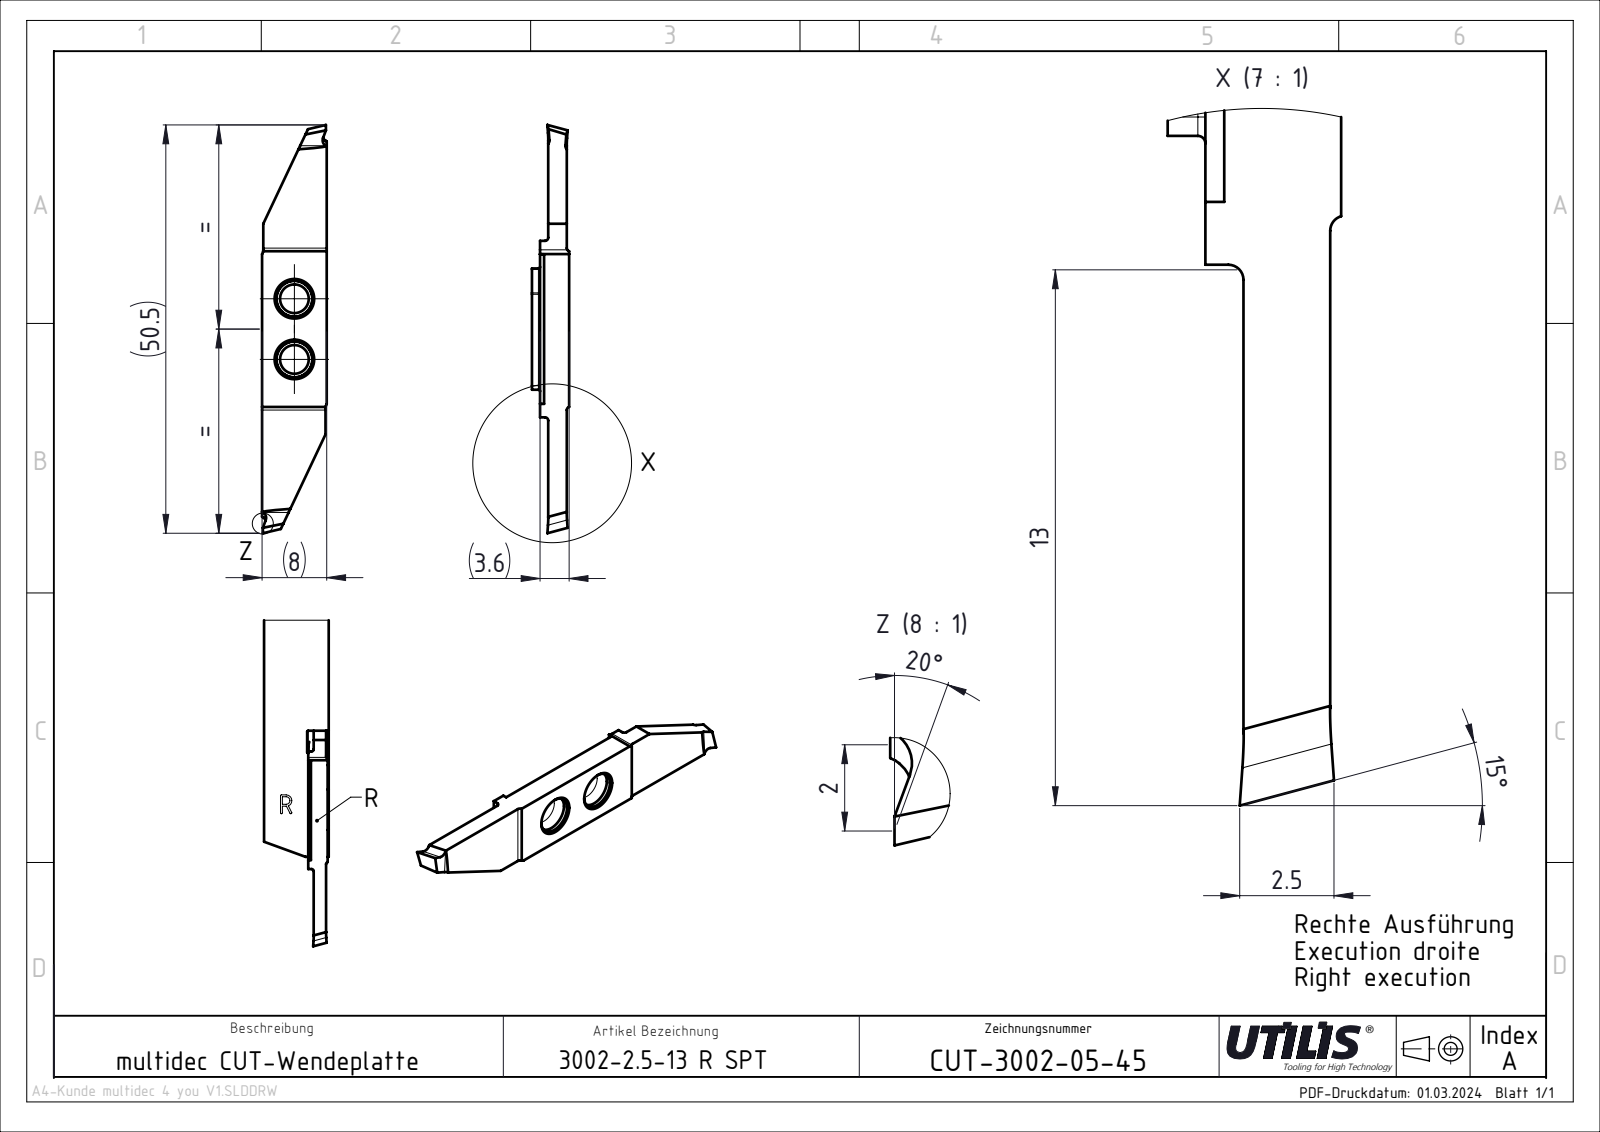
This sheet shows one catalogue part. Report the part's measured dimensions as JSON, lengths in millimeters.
{"part_name": "CUT-3002 SPT Slim_and_Deep; ASME Y14.5", "step_written_by": "SolidWorks 2023 SP4 || FormatWorks Professional (AP242_MANAGED_MODEL_BASED_3D_ENGINEERING_MIM_LF)", "units": "millimeters", "bodies": {"solids": 1, "faces": 36, "planar": 26, "cylindrical": 10, "other": 0}, "overall_size": [50.5, 8, 3.6], "volume_mm3": 899, "surface_area_mm2": 1003, "round_holes": [[3.55, 2]], "partial_cylinders_radius": [[0.4, 4], [1, 2]], "face_to_face_distances": [2.3, 1.01, 3.31, 3.6, 2.59, 8, 18.09, 7.85, 7.7, 21.82], "hole_center_spacings": [7.5]}
